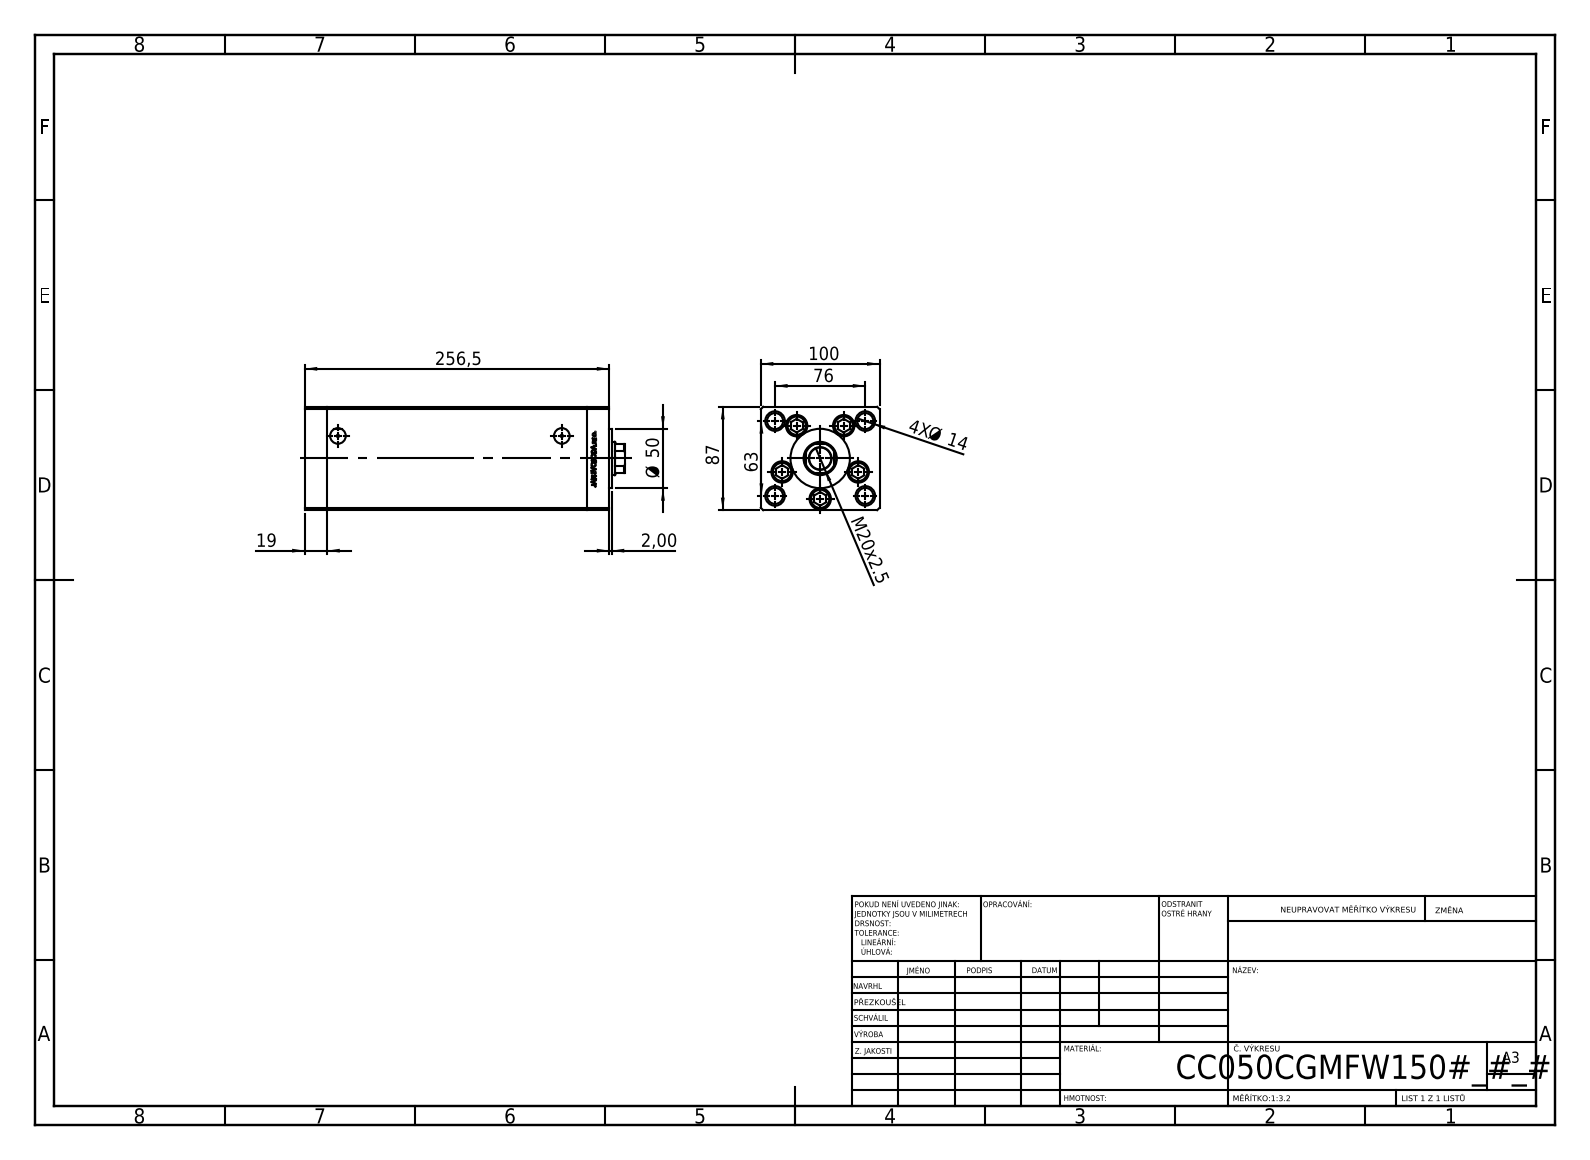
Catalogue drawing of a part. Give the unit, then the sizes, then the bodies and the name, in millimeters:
Units: millimetres
Overall size (bounding box): 269.5 × 100 × 87
Round holes (diameter × count): ⌀13.5 ×9, ⌀18 ×5, ⌀12 ×4, ⌀16.5 ×4, ⌀2 ×2, ⌀13.16 ×2, ⌀17 ×1, ⌀18.5 ×1, ⌀28 ×1
Round bosses / shafts (diameter × count): ⌀8 ×5, ⌀17 ×4, ⌀50 ×1
Partial cylindrical surfaces — rounded edges, fillets, slot ends (radius × count): R0.93 ×2, R13.5 ×1
Main face-to-face distances: 100, 87, 19, 218.5, 237.5, 34.25, 256.5, 222.25, 203.25, 15.25
Hole centre spacings: 34, 49.36, 18.59, 21.03, 38.08, 39.27, 40.83, 43.24
Volume: 1 823 000 mm³ · Surface area: 278 224 mm²
Bodies: 13 solids, 1176 faces (546 planar, 168 cylindrical, 462 other)
Part name (STEP PRODUCT): V220C BACK_C; V220C FRONT; V220C_C MIDDLE; ALLEN BOLT (+1 more)
STEP written by: SolidWorks 2019 (CONFIG_CONTROL_DESIGN)
